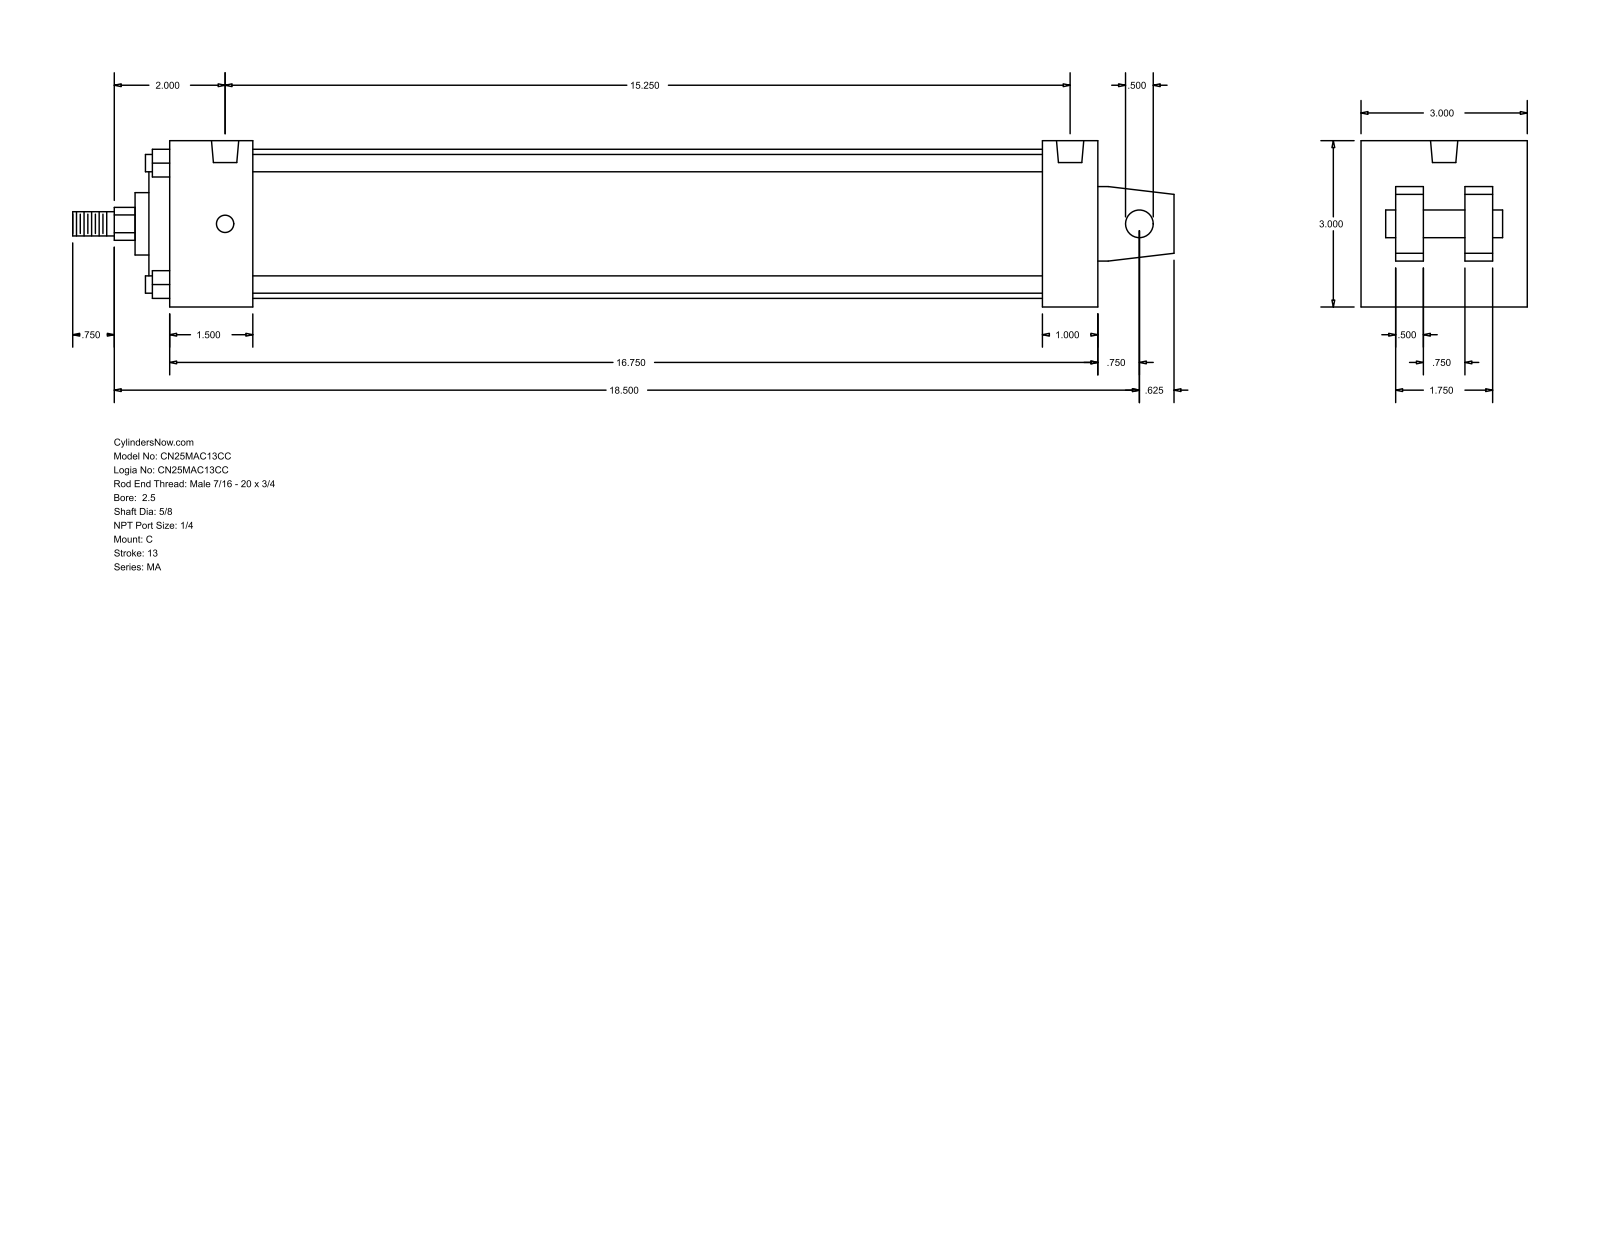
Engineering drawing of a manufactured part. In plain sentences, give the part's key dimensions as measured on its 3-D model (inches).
The part is named "MA_C__0250_0.625". Its 3-D file was written by "GSSL Pune (CONFIG_CONTROL_DESIGN)". It is 0 solids with 105 faces: 77 planar, 28 cylindrical and 0 other. Overall it measures 19.875 by 3 by 3 inches. Round holes: 4 of diameter 0.313, 2 of diameter 0.492. Round bosses or shafts: 4 of diameter 0.313, 1 of diameter 2.69, 1 of diameter 2, 1 of diameter 1.125, 1 of diameter 0.625, 1 of diameter 0.5, 1 of diameter 0.437. Partial cylindrical surfaces (rounded edges, fillets, slot ends): 1 of radius 0.297. The main face-to-face distances are 3, 16.75, 0.5, 0.625, 1.875, 1, 1.5, 15.75, 14.25, 15.25. The hole center spacings are 15.25.
